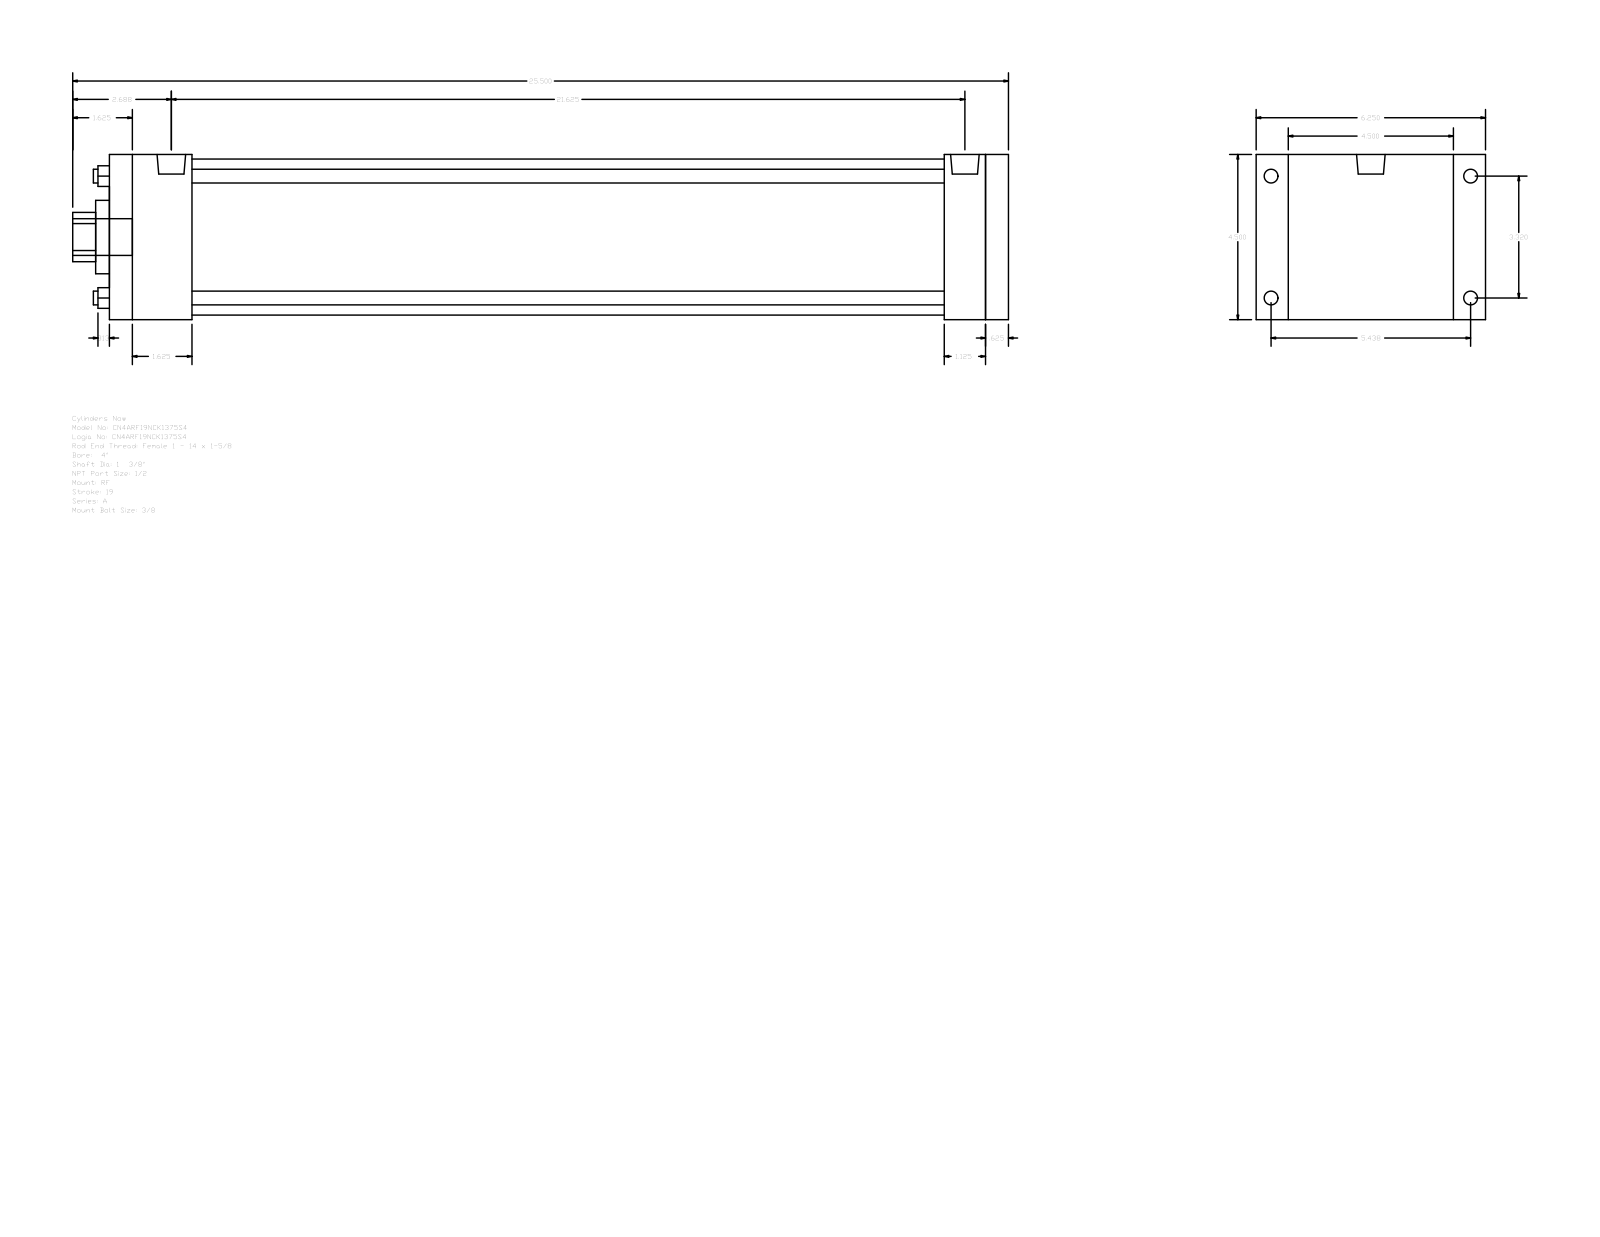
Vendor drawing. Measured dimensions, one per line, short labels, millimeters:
name: A_RF__0400_1.375
written by: GSSL Pune (CONFIG_CONTROL_DESIGN)
unit: mm
bodies: 0 solids, 92 faces (64 planar, 28 cylindrical, 0 other)
size: 647.7 × 158.75 × 114.3
holes: 4× ⌀9.53, 1× ⌀34.92, 1× ⌀50.8, 1× ⌀107.95
bosses: 4× ⌀9.53, 4× ⌀8.73, 2× ⌀19.77, 1× ⌀25.4
rounds: 1× R17.06
face distances: 114.3, 622.3, 15.87, 606.43, 28.58, 22.23, 136.53, 577.85, 44.45, 57.15
hole spacings: 59.62, 84.32, 119.25
